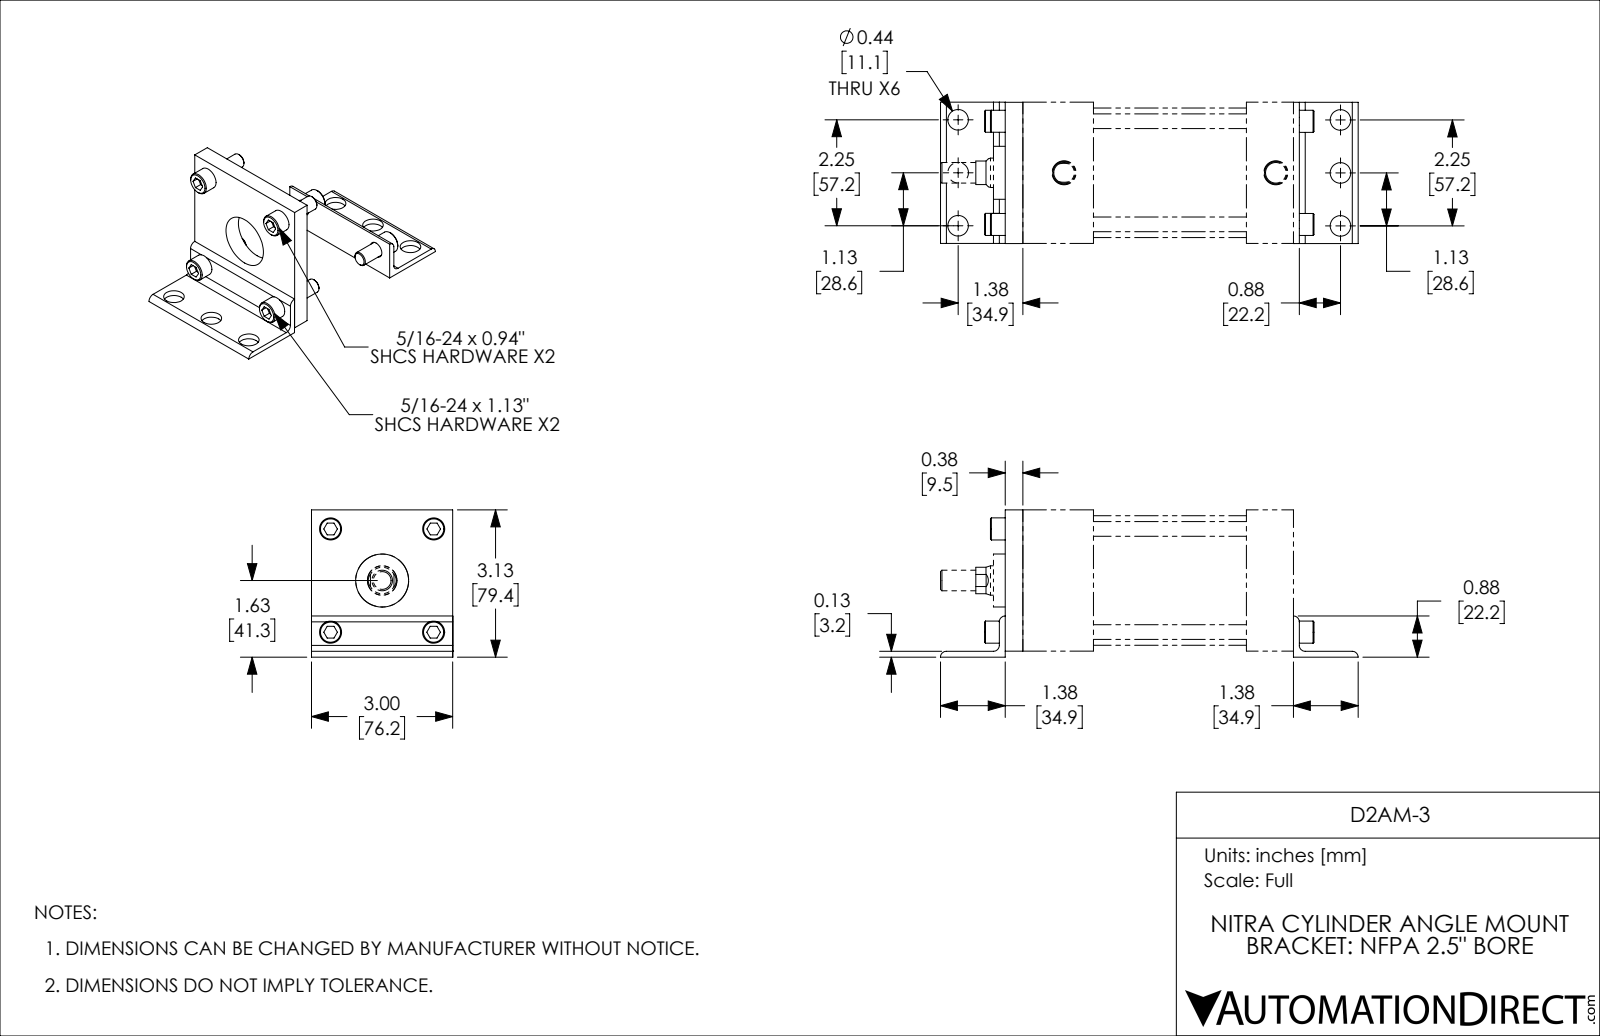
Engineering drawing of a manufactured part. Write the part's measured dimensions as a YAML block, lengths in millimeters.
part_name: "D240020DT-M_2; D2AM-3_2; D240020DT-M_PISTON_KK1; D2AM-3 (+2 more)"
step_written_by: "SolidWorks 2019 (CONFIG_CONTROL_DESIGN)"
units: millimeters
bodies: {solids: 11, faces: 362, planar: 136, cylindrical: 122, other: 104}
overall_size: [225.4, 79.4, 76.3]
volume: 627300
surface_area: 152600
round_holes:
  - {diameter: 8.7, count: 6}
  - {diameter: 11.1, count: 6}
  - {diameter: 6.9, count: 4}
  - {diameter: 8, count: 4}
  - {diameter: 12.7, count: 4}
  - {diameter: 11.1, count: 2}
  - {diameter: 15.9, count: 1}
  - {diameter: 28.6, count: 1}
  - {diameter: 47.6, count: 1}
  - {diameter: 63.5, count: 1}
round_bosses_or_shafts:
  - {diameter: 7.9, count: 10}
  - {diameter: 11.9, count: 6}
  - {diameter: 69.9, count: 1}
  - {diameter: 63.5, count: 1}
  - {diameter: 28.6, count: 1}
  - {diameter: 15.8, count: 1}
  - {diameter: 11.1, count: 1}
partial_cylinders:
  - {radius: 3.2, count: 6}
  - {radius: 7.1, count: 1}
face_to_face_distances: [76.2, 120.7, 146.1, 25.4, 155.6, 130.2, 9.5, 82.6, 108, 38.1]
hole_center_spacings: [55.7, 78.7, 39.3, 55.6, 55.7, 78.7, 57.2, 206.4]
